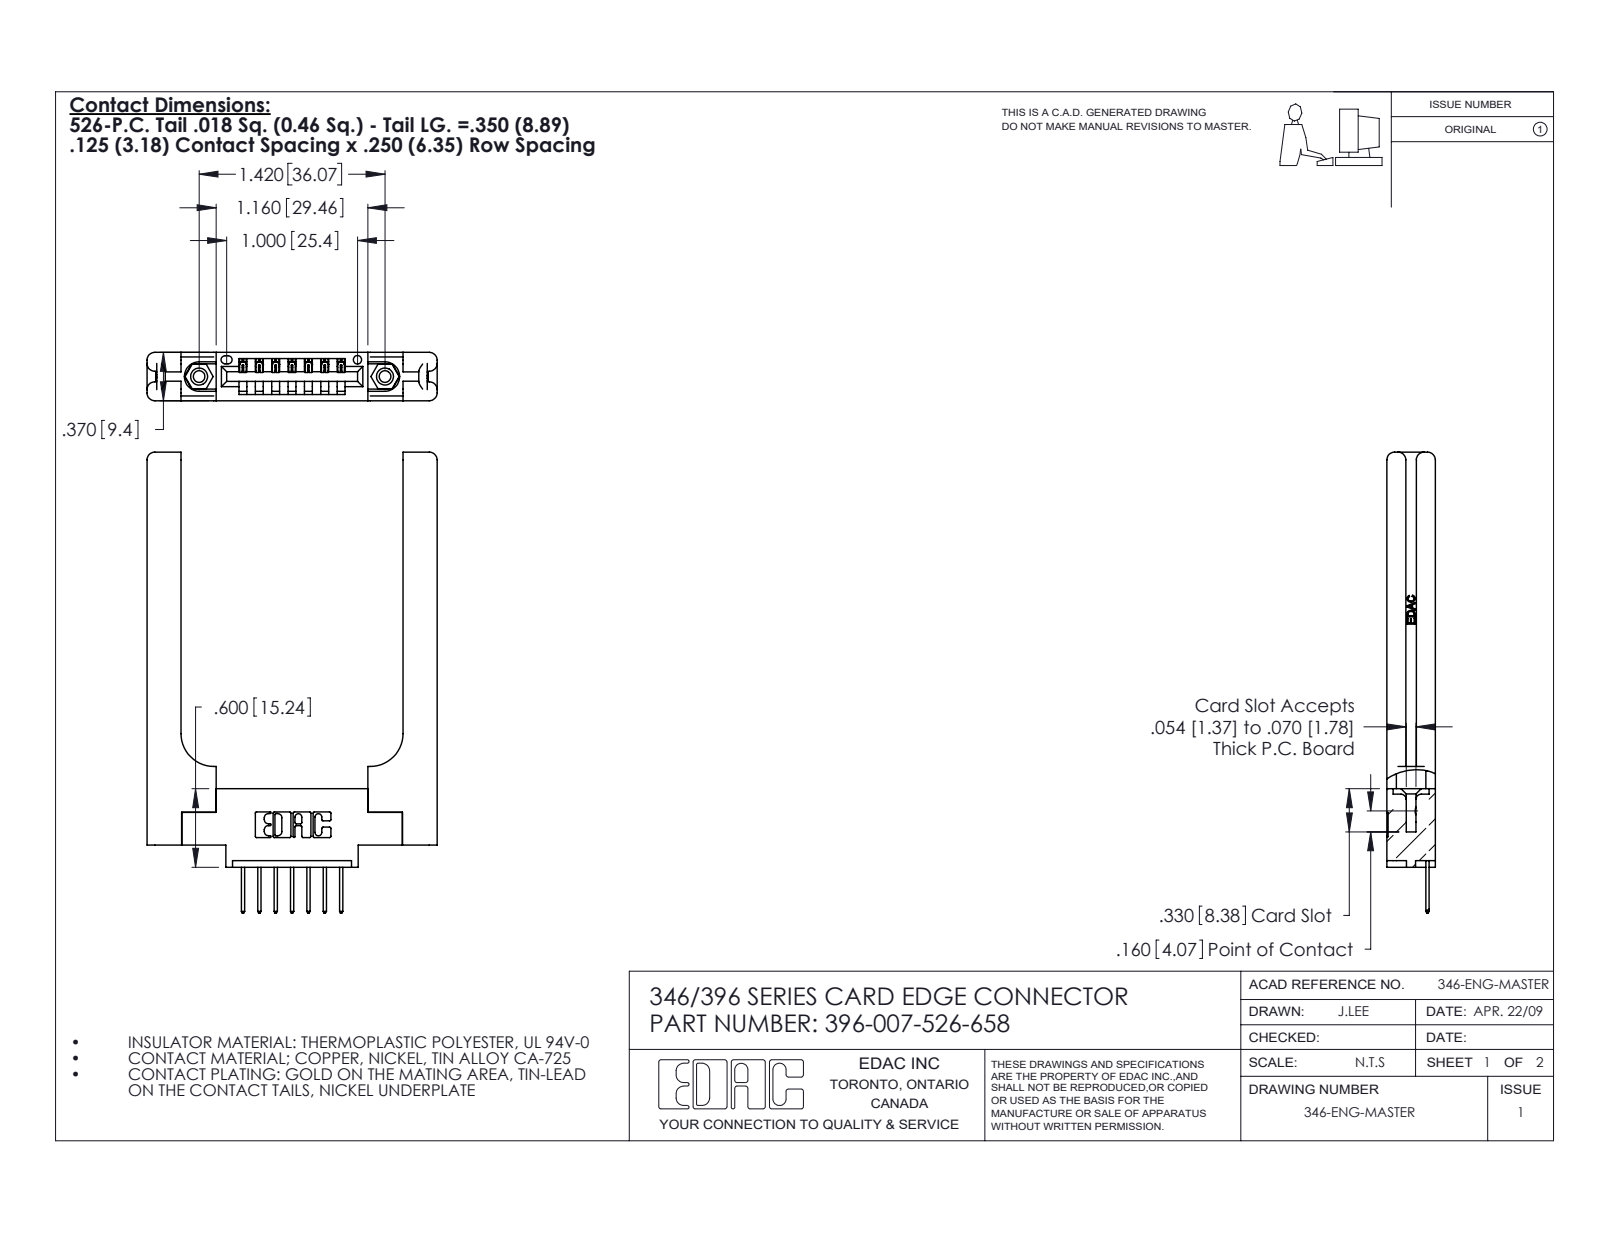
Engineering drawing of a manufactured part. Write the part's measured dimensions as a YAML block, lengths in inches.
part_name: "345-292-001_345-293-126; 396-007-526-658; 345-250-001_345-250-001-102; 346 Part_0.170 Offset - 0.156 Dia-TH (+1 more)"
step_written_by: "SolidWorks 2020 (CONFIG_CONTROL_DESIGN)"
units: inches
bodies: {solids: 12, faces: 802, planar: 522, cylindrical: 220, other: 60}
overall_size: [3.52, 2.216, 0.37]
volume: 0.762
surface_area: 17.34
round_holes:
  - {diameter: 0.089, count: 2}
  - {diameter: 0.125, count: 2}
  - {diameter: 0.156, count: 2}
  - {diameter: 0.064, count: 1}
round_bosses_or_shafts:
  - {diameter: 0.155, count: 2}
partial_cylinders:
  - {radius: 0.01, count: 22}
  - {radius: 0.06, count: 16}
  - {radius: 0.006, count: 14}
  - {radius: 0.01, count: 14}
  - {radius: 0.007, count: 6}
  - {radius: 0.031, count: 6}
  - {radius: 0.026, count: 3}
  - {radius: 0.03, count: 2}
face_to_face_distances: [0.37, 0.15, 0.22, 0.072, 0.148, 0.25, 1.696, 0.102, 0.048, 0.322]
hole_center_spacings: [0.246, 1.217, 1.42]
